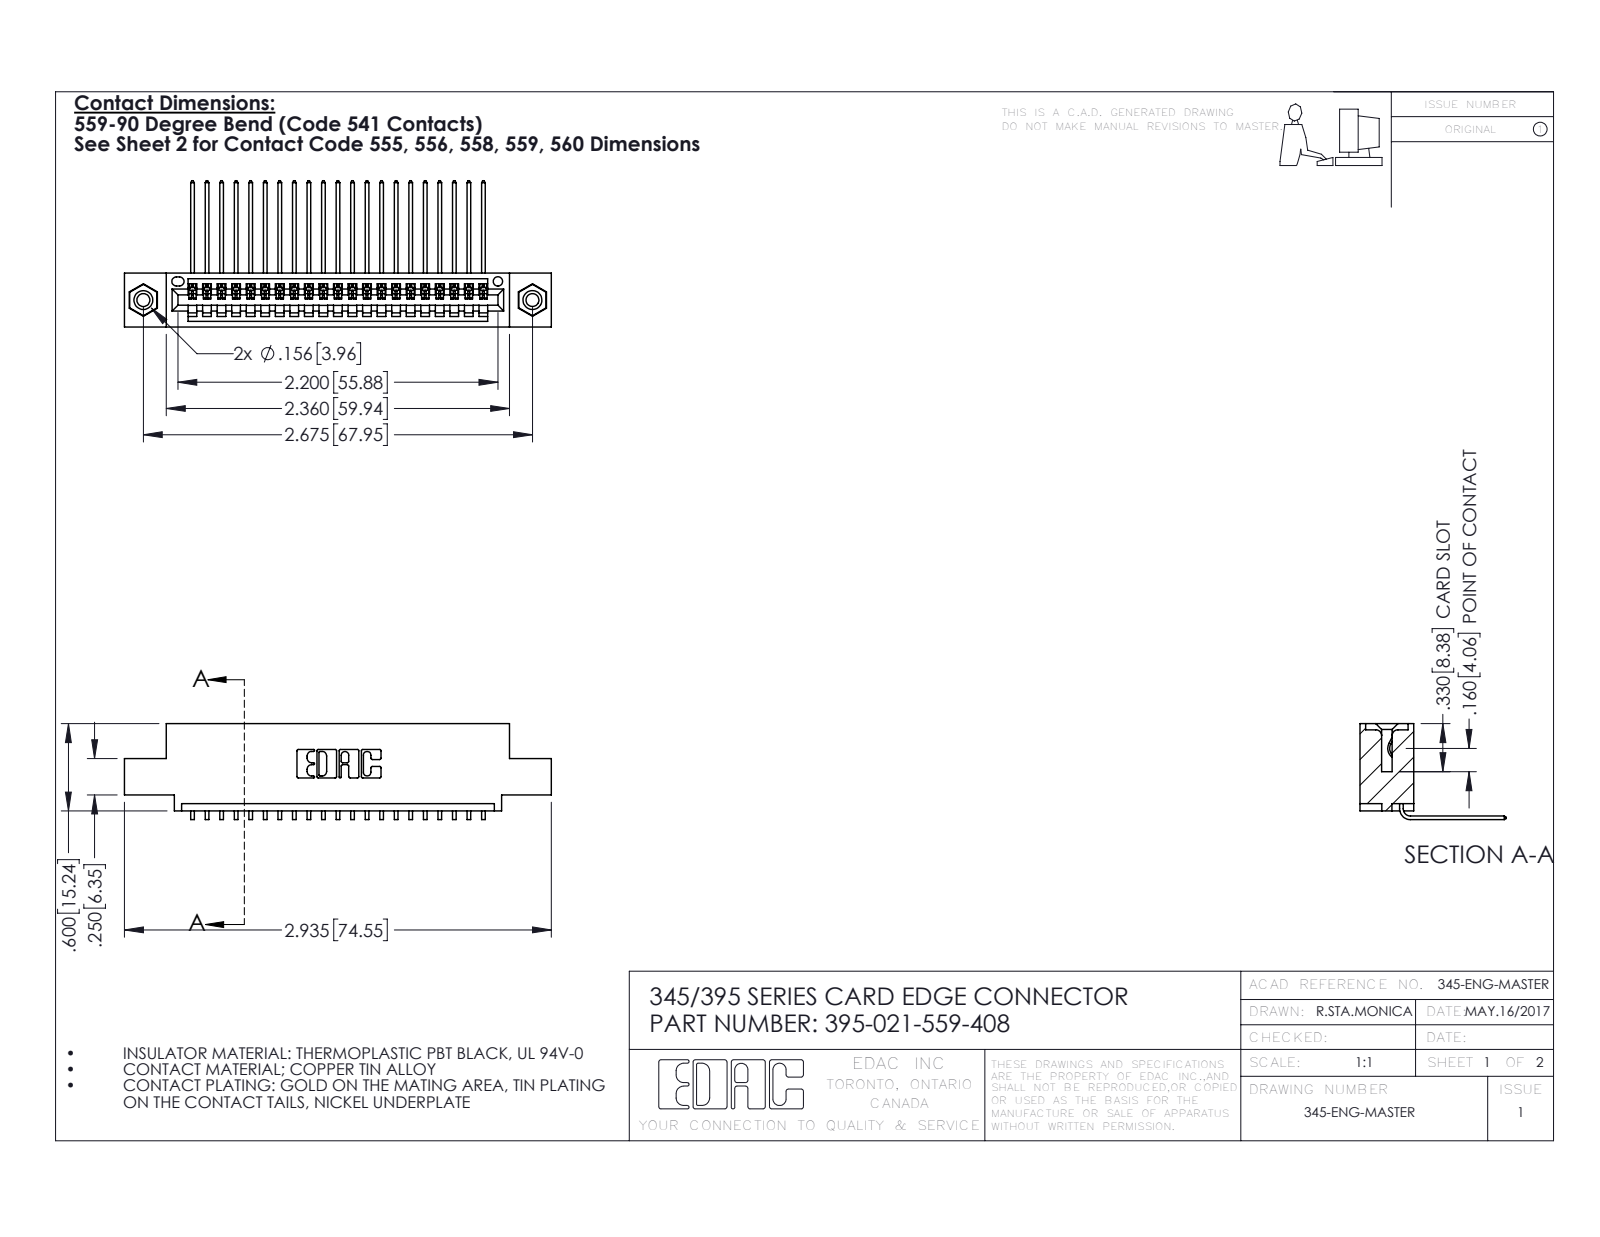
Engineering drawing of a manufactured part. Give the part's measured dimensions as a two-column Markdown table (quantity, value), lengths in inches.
| quantity | value |
| --- | --- |
| part name | 395-021-559-408; 345-250-001_345-250-003-102; 345 Part_0.110 Offset - 0.156 Dia-TI; 345-292-001_558 559 Tail - 1 |
| STEP written by | SolidWorks 2016 (CONFIG_CONTROL_DESIGN) |
| units | inches |
| bodies | 24 solids, 1450 faces (998 planar, 436 cylindrical, 16 other) |
| overall size | 2.935 × 1.005 × 0.659 |
| volume | 0.421 in³ |
| surface area | 14.56 in² |
| round holes (diameter × count) | 0.089 × 2, 0.125 × 2, 0.156 × 2, 0.064 × 1 |
| round bosses / shafts (diameter × count) | 0.155 × 2 |
| partial cylindrical surfaces (radius × count) | 0.006 × 42, 0.01 × 22, 0.007 × 6, 0.031 × 6, 0.026 × 3, 0.031 × 2, 0.04 × 2, 0.014 × 1 |
| main face-to-face distances | 0.072, 0.298, 0.37, 0.2, 0.098, 0.272, 0.025, 0.225, 0.149, 0.072 |
| hole center spacings | 0.27, 2.441, 2.675 |
